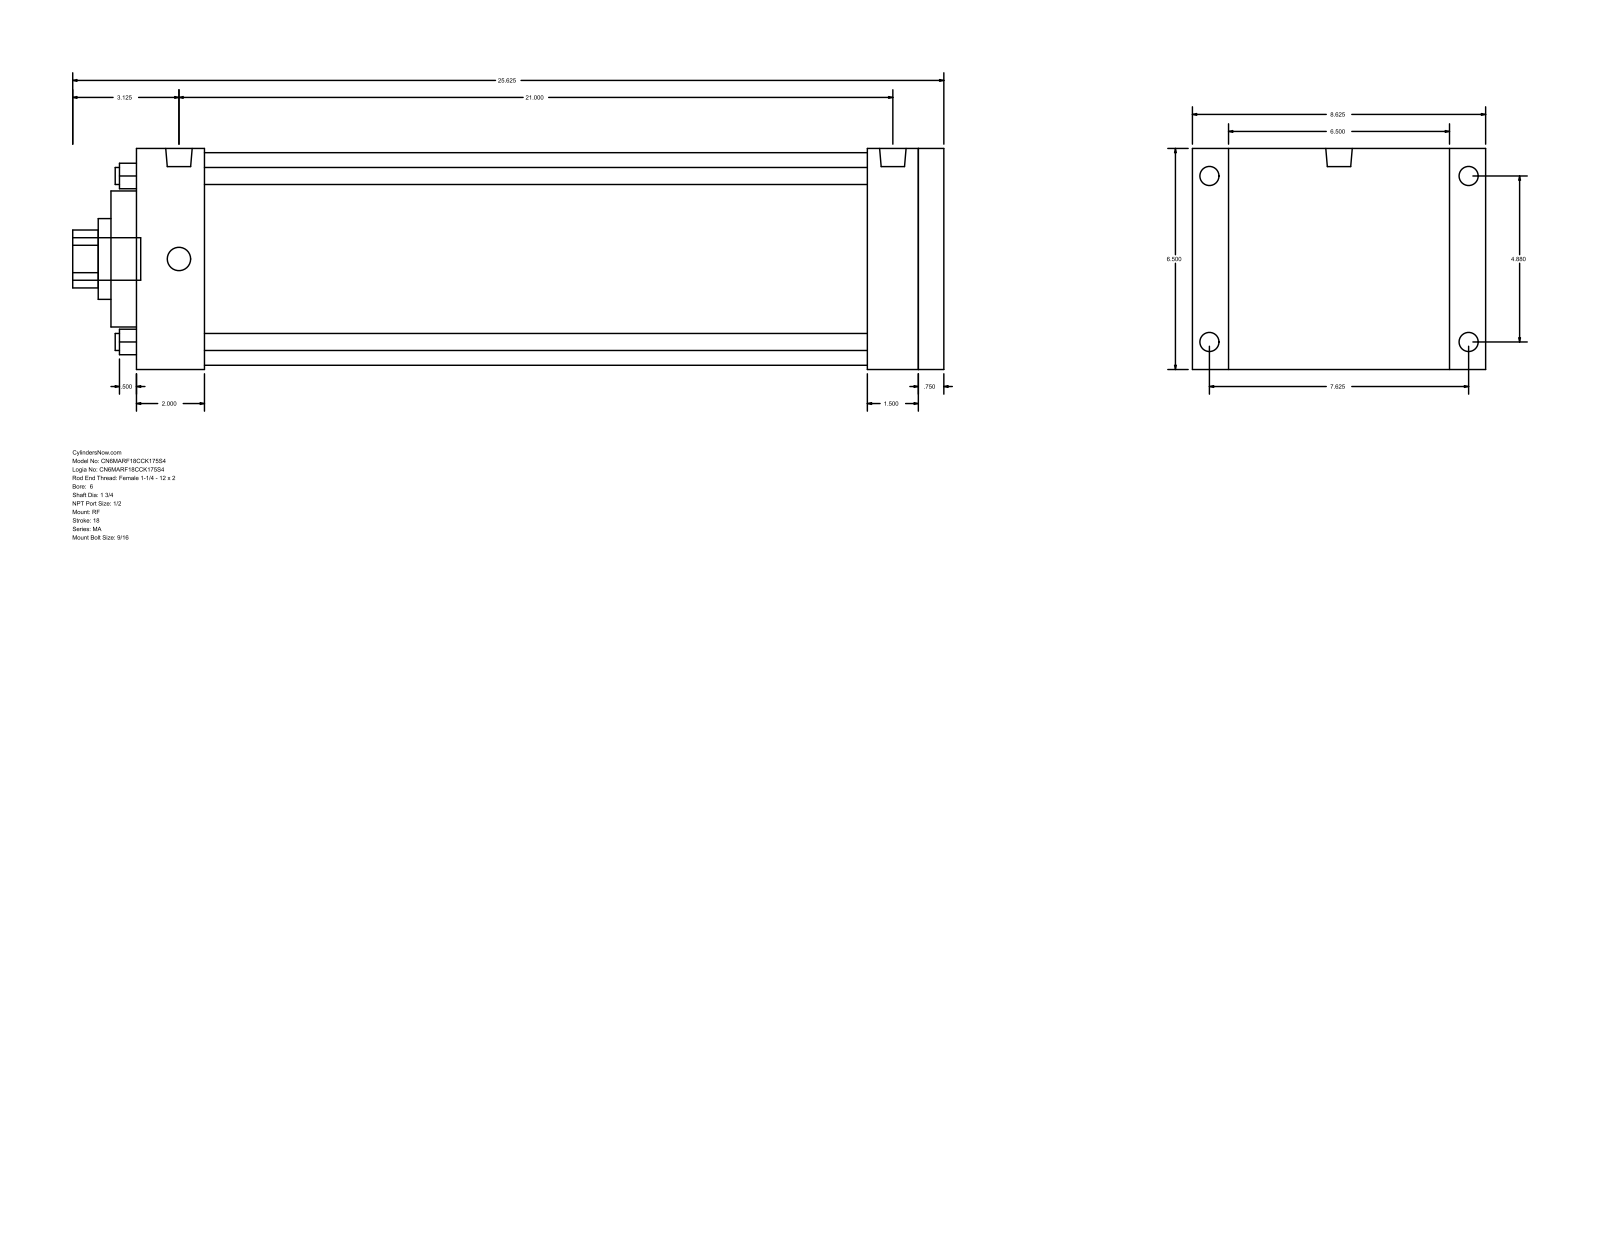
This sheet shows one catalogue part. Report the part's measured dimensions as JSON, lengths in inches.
{"part_name": "MA_RF__0600_1.75", "step_written_by": "GSSL Pune (CONFIG_CONTROL_DESIGN)", "units": "inches", "bodies": {"solids": 0, "faces": 94, "planar": 65, "cylindrical": 29, "other": 0}, "overall_size": [25.625, 8.625, 6.5], "round_holes": [[0.5, 4], [1.75, 1], [2.375, 1], [4, 1], [6.25, 1]], "round_bosses_or_shafts": [[0.687, 4], [0.563, 4], [0.778, 2], [1.25, 1]], "partial_cylinders_radius": [[0.852, 1]], "face_to_face_distances": [6.5, 23.75, 0.75, 23, 1.5, 2, 21, 21.75, 21.5, 19.5], "hole_center_spacings": [3.451, 4.88, 6.902]}
